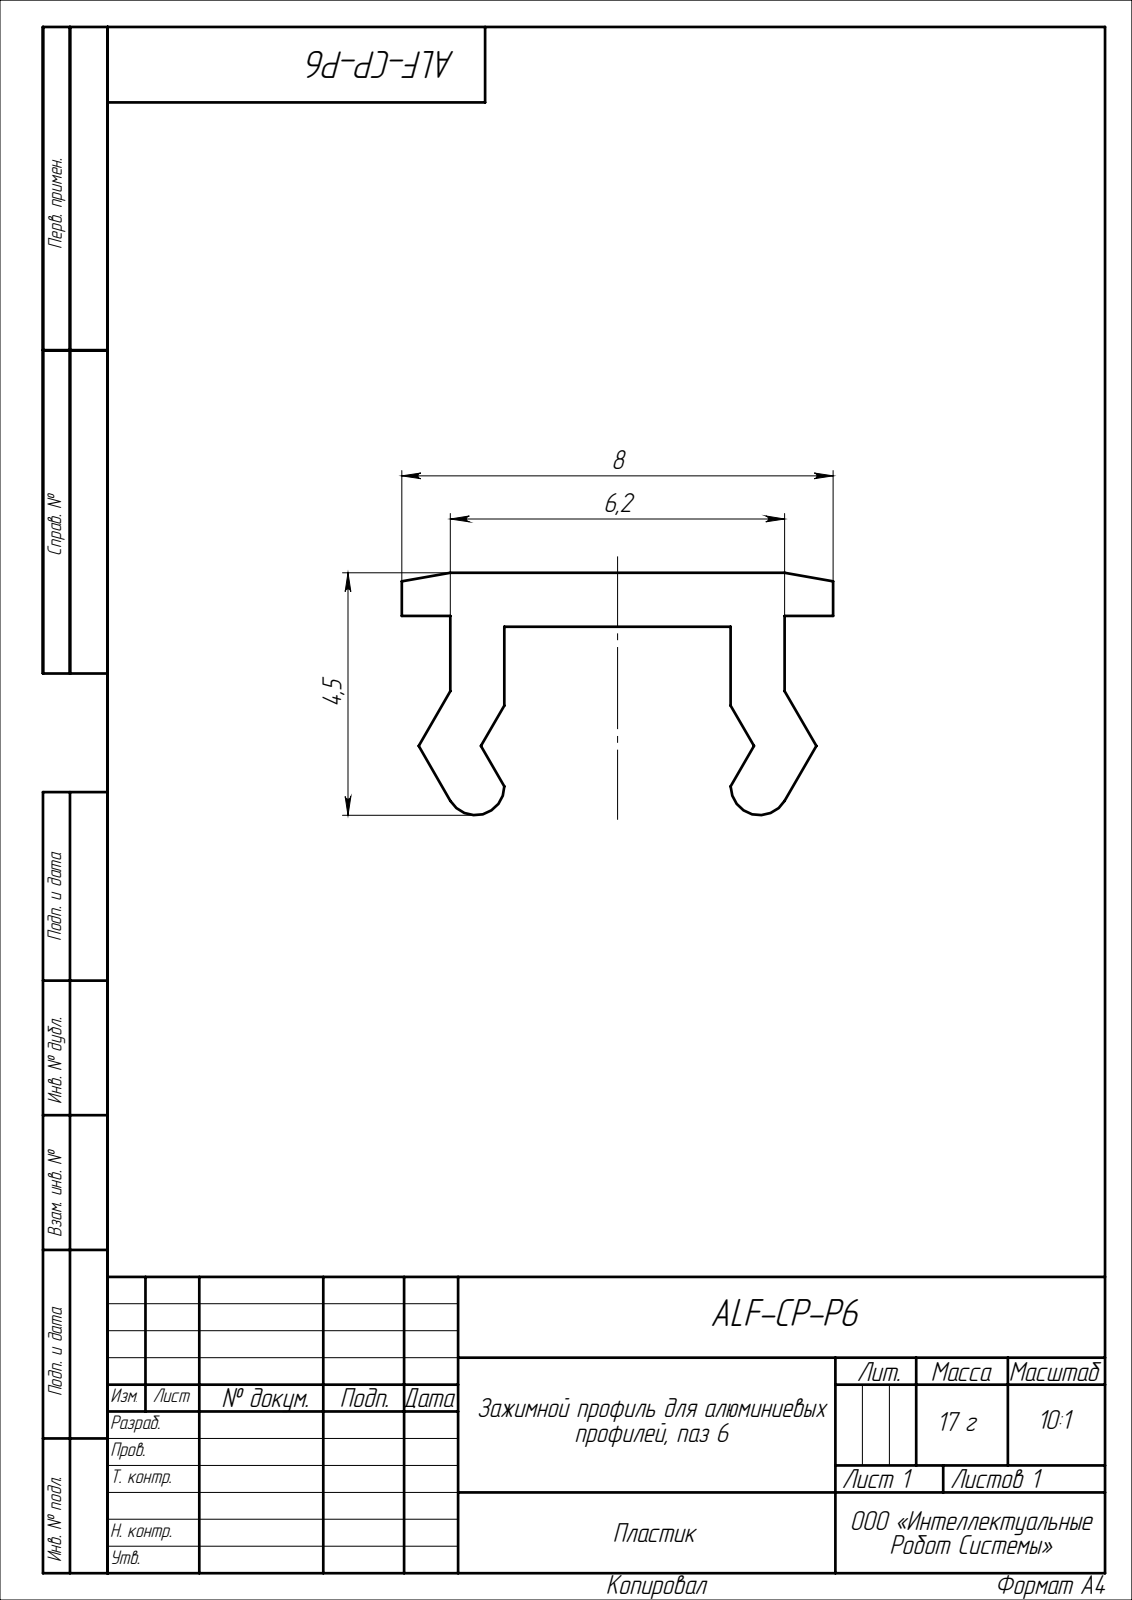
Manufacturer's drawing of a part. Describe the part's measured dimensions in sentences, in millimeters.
The part is named "ALF-CP-P6". Its 3-D file was written by "SolidWorks 2022 (CONFIG_CONTROL_DESIGN)". It is 1 solid with 24 faces: 22 planar, 2 cylindrical and 0 other. Overall it measures 1000 by 8 by 4.5 millimeters. Its volume is 14 849 cubic millimeters and its surface area 32 032 square millimeters. Partial cylindrical surfaces (rounded edges, fillets, slot ends): 2 of radius 0.54. The main face-to-face distances are 1, 5.39, 5.2, 6.39, 0.8, 4.39, 4.2, 6.2, 0.9, 1.9.
